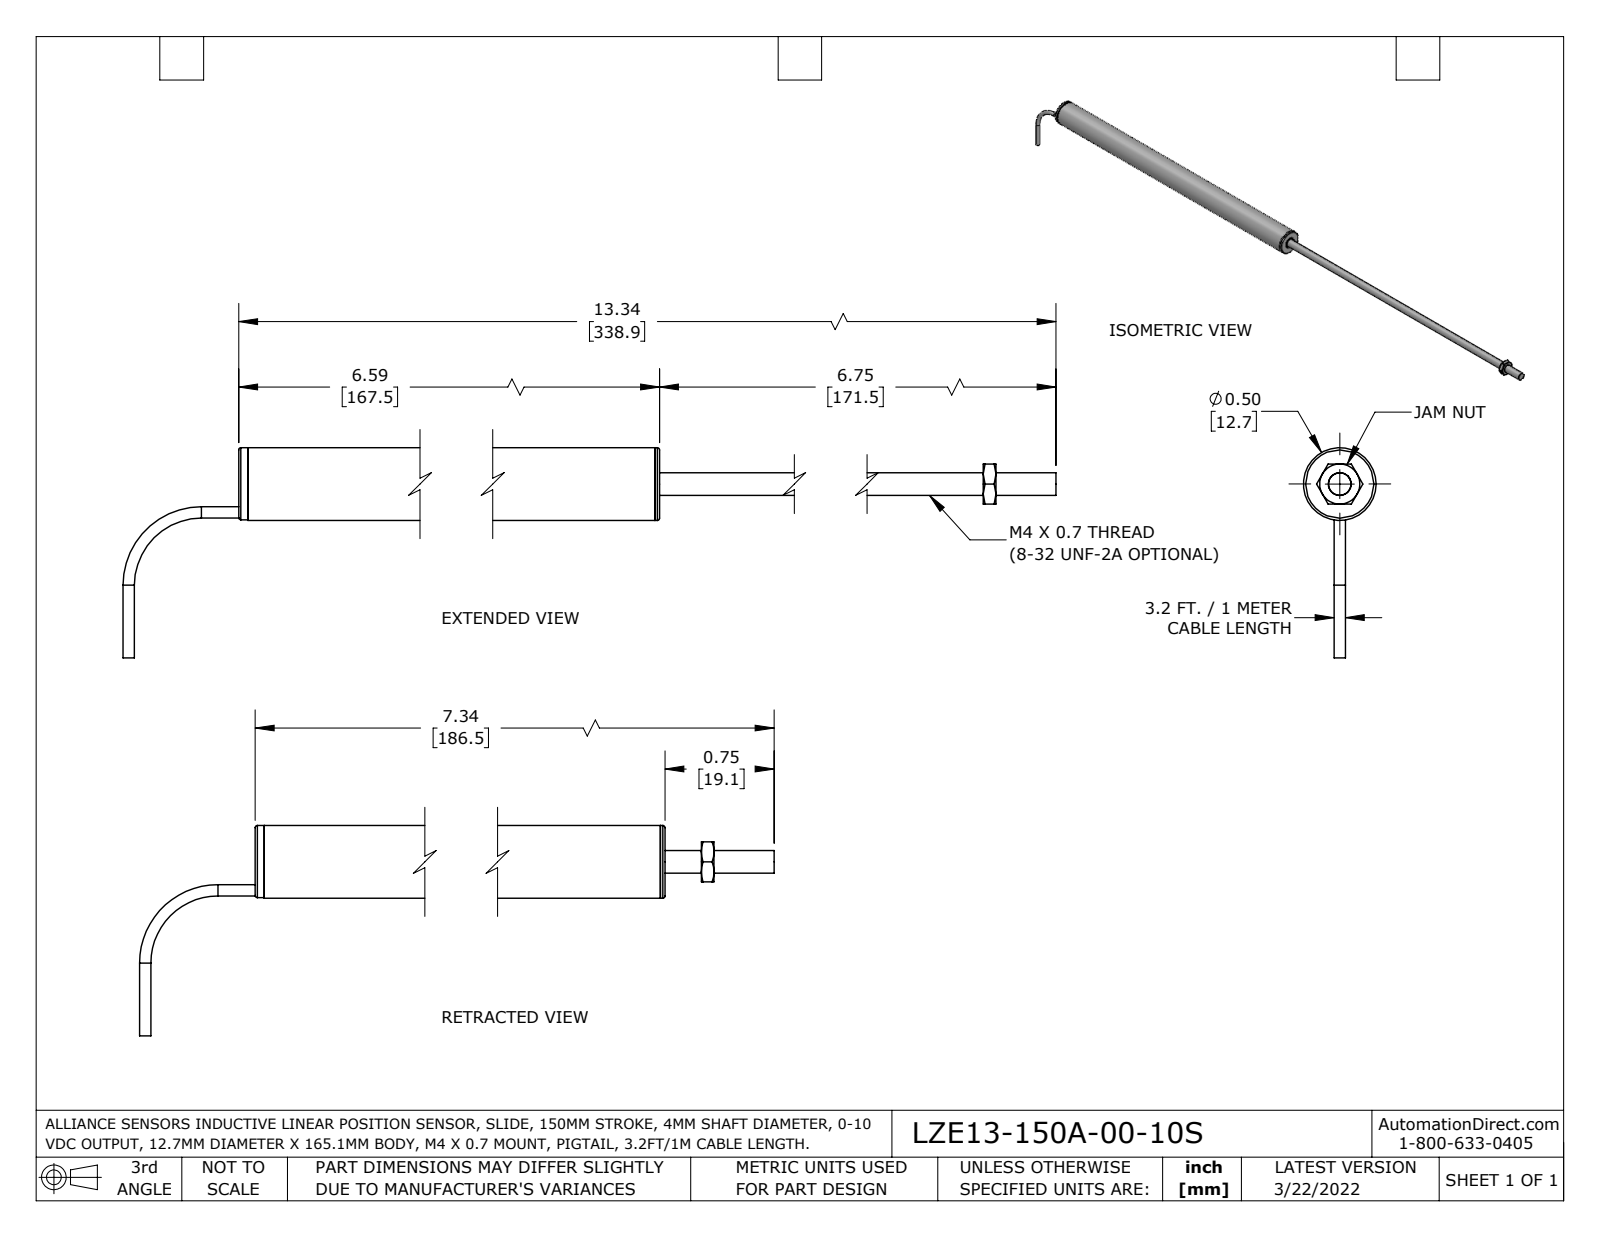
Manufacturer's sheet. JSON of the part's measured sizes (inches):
{"part_name": "3120-0031; 3120-0032; 3120-0034-XX-Z_3120-0034-06-Z; 3120-0040_SHRINK (+6 more)", "step_written_by": "SolidWorks 2021 (AUTOMOTIVE_DESIGN)", "units": "inches", "bodies": {"solids": 9, "faces": 98, "planar": 32, "cylindrical": 38, "other": 28}, "overall_size": [14.139, 1.445, 0.5], "volume_in3": 0.429, "surface_area_in2": 34.44, "round_holes": [[0.078, 1], [0.157, 1], [0.187, 1], [0.223, 1]], "round_bosses_or_shafts": [[0.5, 1], [0.468, 1], [0.222, 1], [0.156, 1], [0.1, 1], [0.078, 1]], "partial_cylinders_radius": [[0.047, 1]], "face_to_face_distances": [0.079, 6.5, 0.031, 0.062, 0.276, 6.594, 6.532, 6.438, 0.094, 6.469], "hole_center_spacings": [0.195]}
